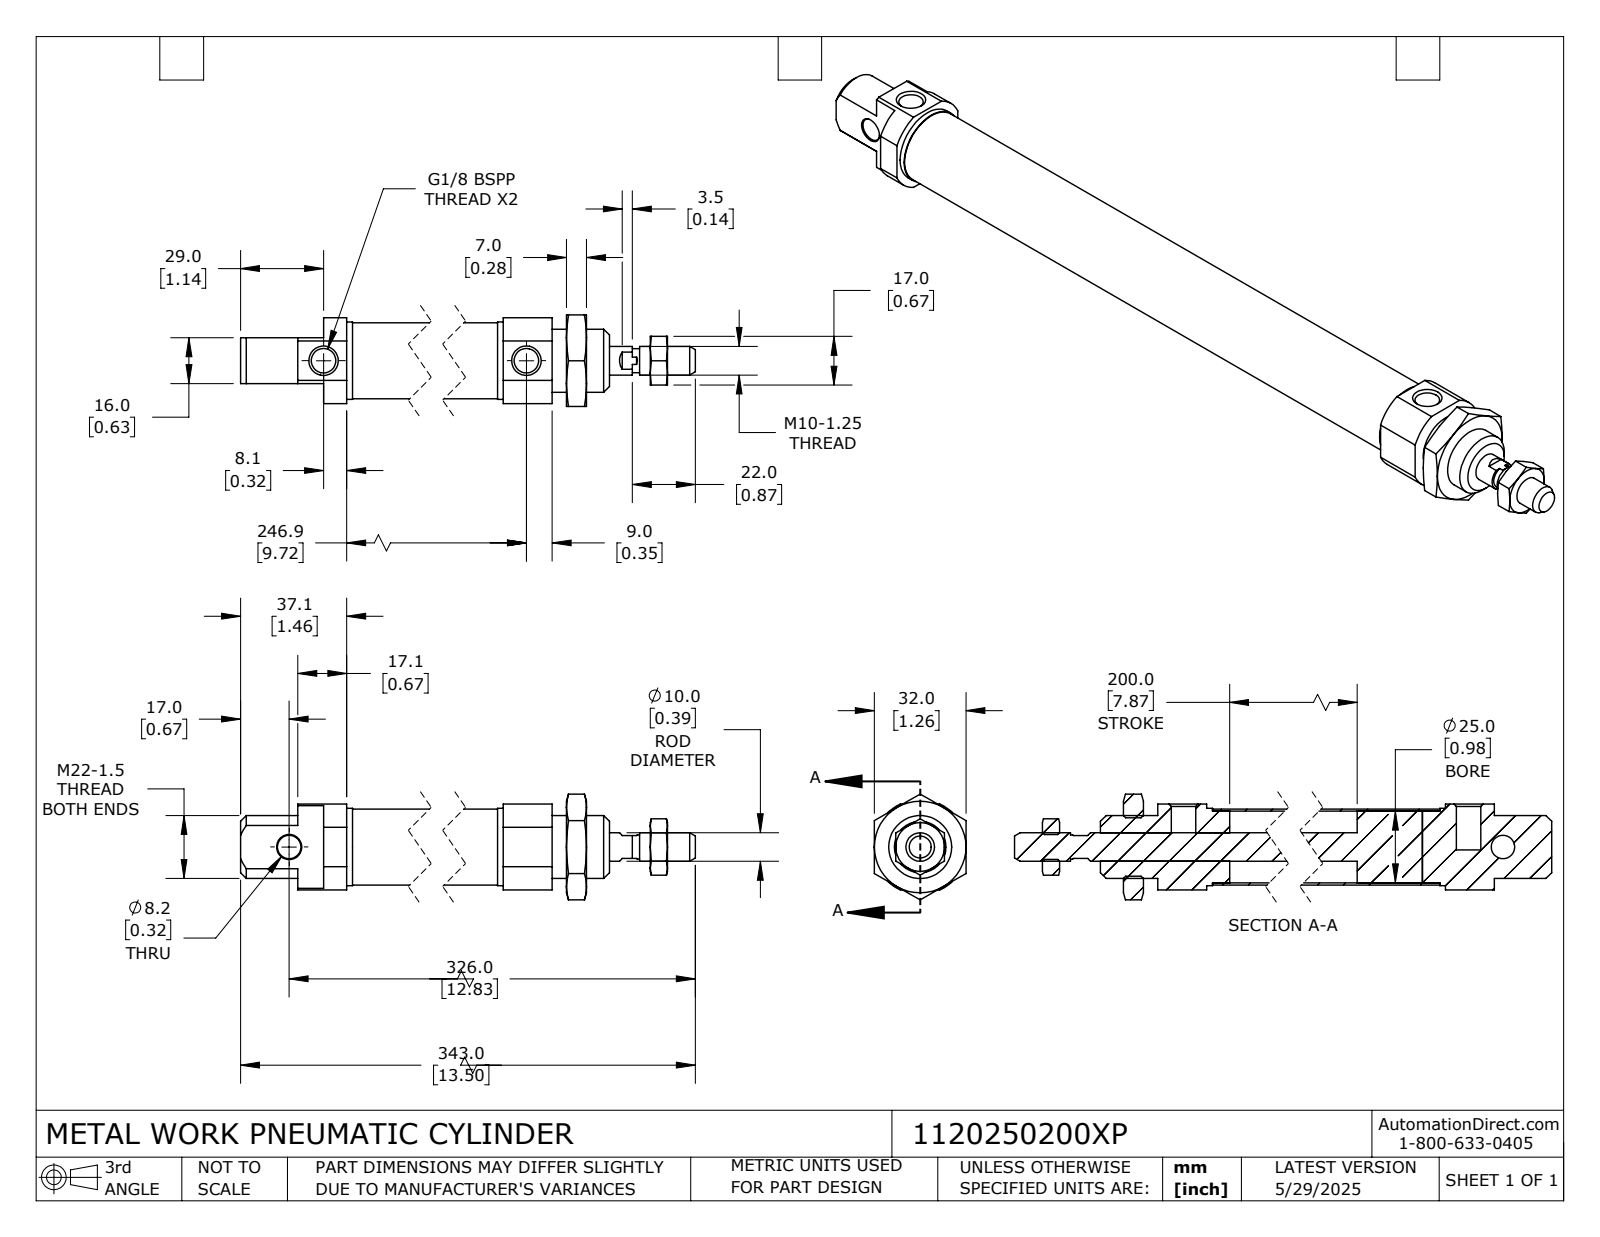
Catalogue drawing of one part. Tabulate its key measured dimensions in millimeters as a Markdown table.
| quantity | value |
| --- | --- |
| part name | 1120250200XP_ROD; 1120250200XP; 1120250200XP_BODY |
| STEP written by | SolidWorks 2024 (CONFIG_CONTROL_DESIGN) |
| units | millimeters |
| bodies | 6 solids, 144 faces (54 planar, 44 cylindrical, 46 other) |
| overall size | 343 × 36.95 × 32 |
| volume | 92 625 mm³ |
| surface area | 65 212 mm² |
| round holes (diameter × count) | 8.57 × 2, 8.2 × 1, 8.65 × 1, 20.38 × 1, 25 × 1 |
| round bosses / shafts (diameter × count) | 27 × 1, 26.52 × 1, 25.15 × 1, 22 × 1, 10 × 1, 8.4 × 1 |
| partial cylindrical surfaces (radius × count) | 16.5 × 1 |
| main face-to-face distances | 7, 8, 37.1, 23, 30, 267.9, 247.9, 25.1, 16, 230.8 |
| hole center spacings | 255 |
